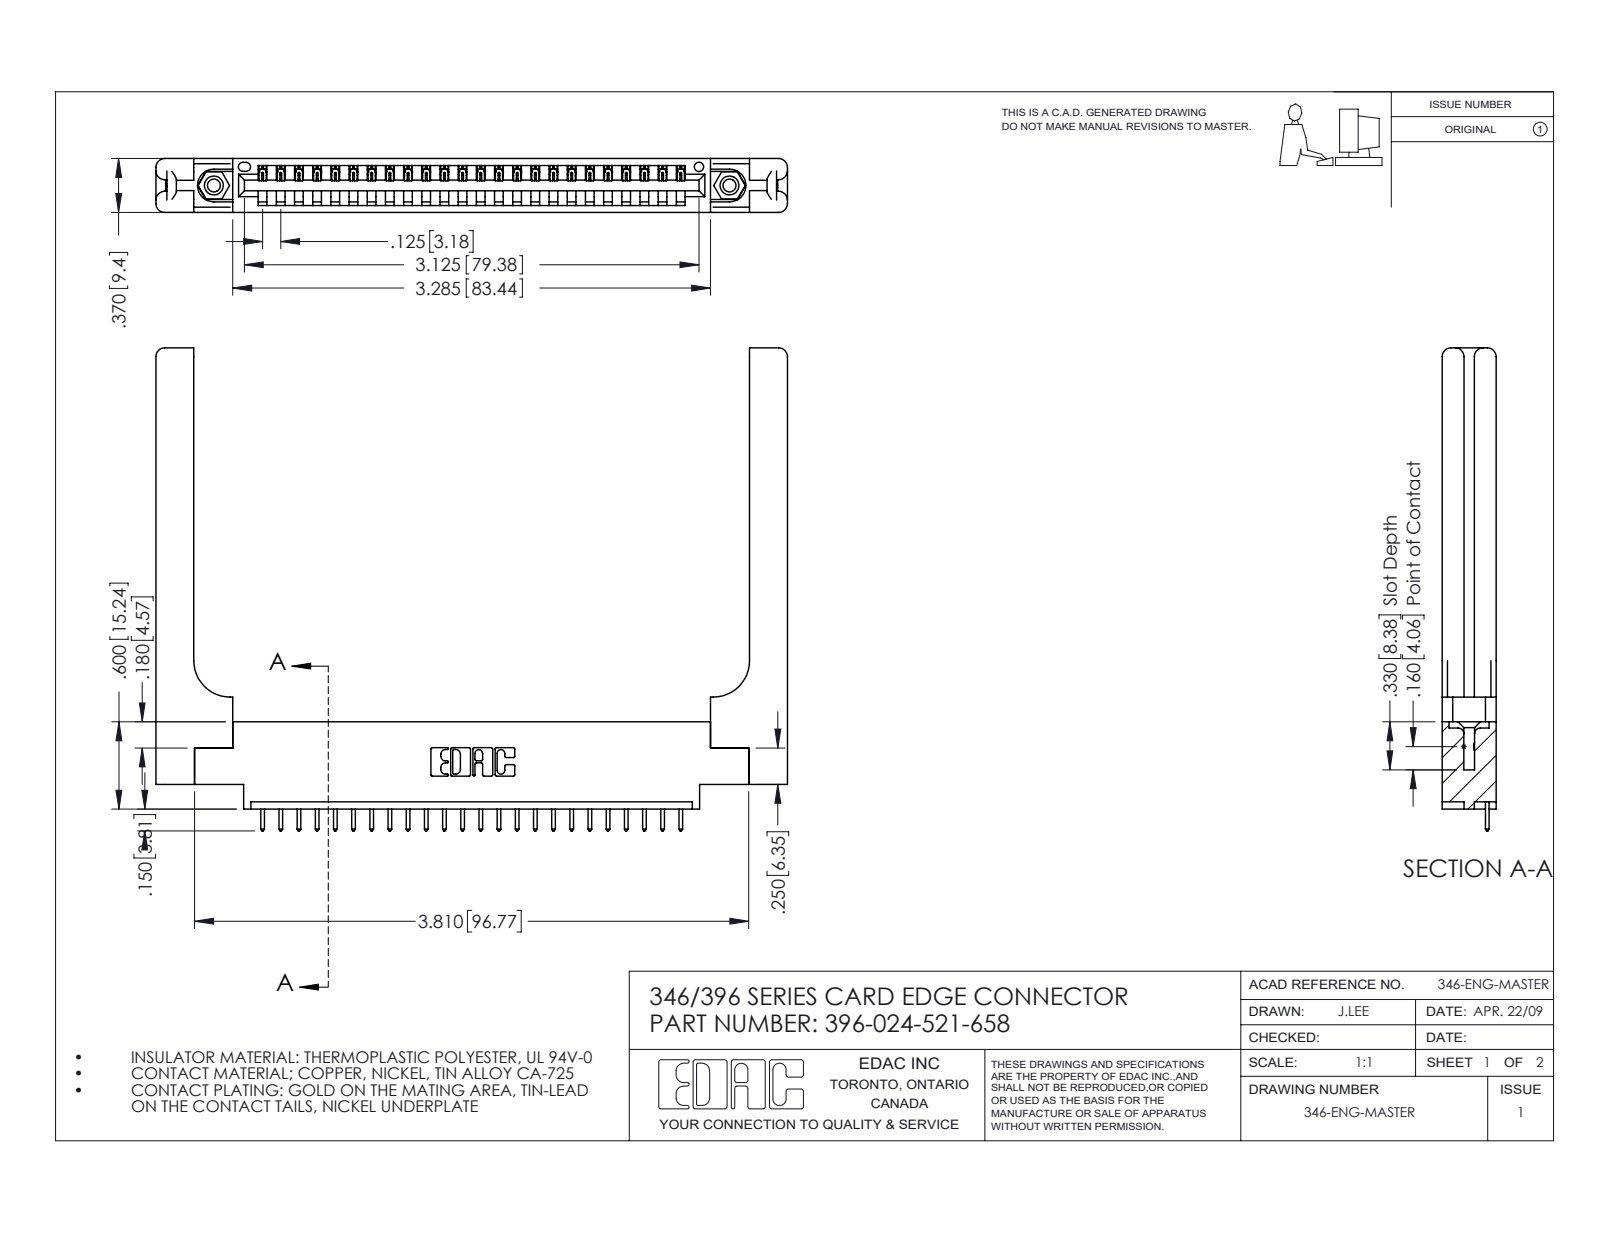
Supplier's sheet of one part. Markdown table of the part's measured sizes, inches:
| quantity | value |
| --- | --- |
| part name | 346-220-058_345-220-058; 396-024-521-658; 346 Part_0.170 Offset - 0.156 Dia-TH; 345-292-001_345-293-121 (+1 more) |
| STEP written by | SolidWorks 2016 (CONFIG_CONTROL_DESIGN) |
| units | inches |
| bodies | 29 solids, 1774 faces (1188 planar, 526 cylindrical, 60 other) |
| overall size | 4.341 × 3.32 × 0.37 |
| volume | 1.082 in³ |
| surface area | 27.31 in² |
| round holes (diameter × count) | 0.089 × 2, 0.125 × 2, 0.156 × 2, 0.064 × 1 |
| round bosses / shafts (diameter × count) | 0.155 × 2 |
| partial cylindrical surfaces (radius × count) | 0.006 × 48, 0.01 × 48, 0.01 × 22, 0.06 × 16, 0.007 × 6, 0.031 × 6, 0.026 × 3, 0.03 × 2 |
| main face-to-face distances | 0.37, 0.072, 0.048, 0.322, 0.15, 0.148, 0.25, 0.298, 0.025, 0.102 |
| hole center spacings | 0.246, 3.337, 3.545 |
